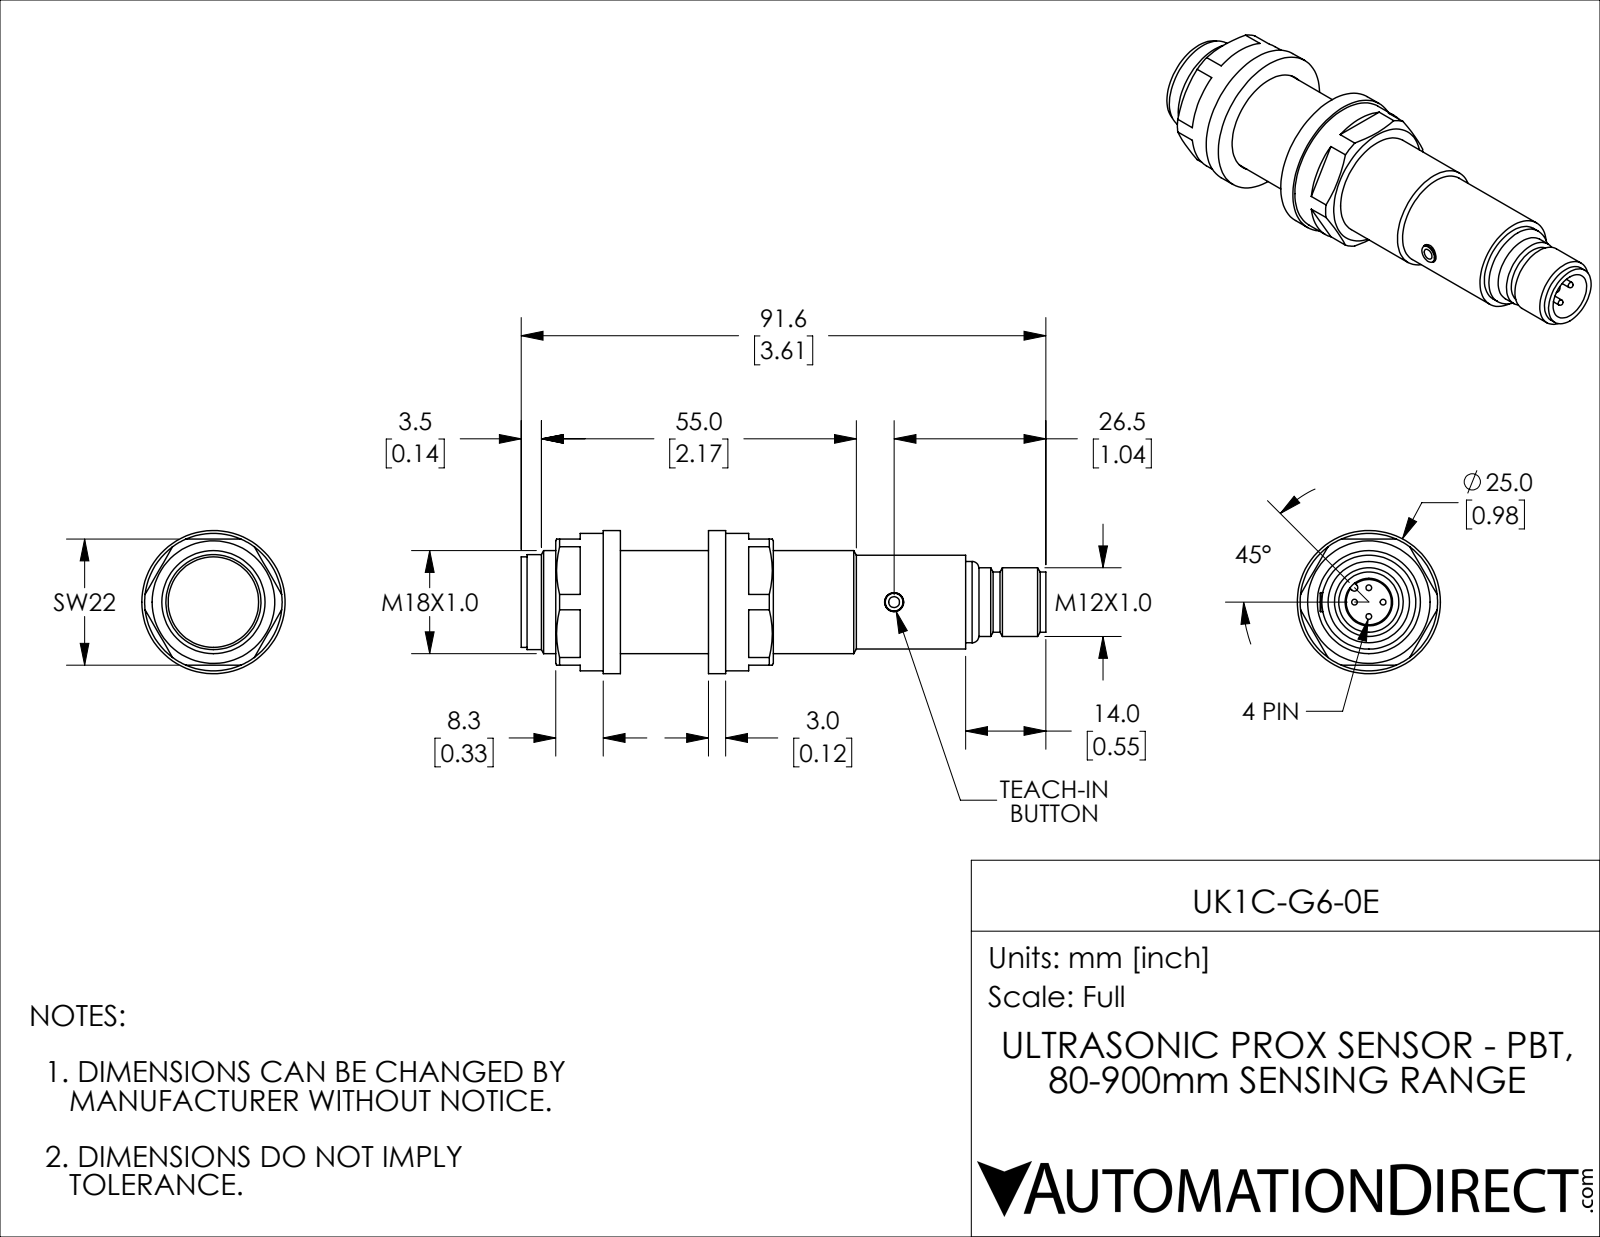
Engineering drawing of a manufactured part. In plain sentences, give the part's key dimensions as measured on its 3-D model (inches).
The part is named "UK1C-G6-0E". Its 3-D file was written by "SolidWorks 2018 (AUTOMOTIVE_DESIGN)". It is 6 solids with 123 faces: 43 planar, 49 cylindrical and 31 other. Overall it measures 3.606 by 0.984 by 0.984 inches. Its volume is 1.477 cubic inches and its surface area 16.01 square inches. Round holes: 1 of diameter 0.13, 1 of diameter 0.327, 1 of diameter 0.709, 1 of diameter 0.717. Round bosses or shafts: 4 of diameter 0.039, 1 of diameter 0.984, 1 of diameter 0.945, 1 of diameter 0.654, 1 of diameter 0.646, 1 of diameter 0.622, 1 of diameter 0.559, 1 of diameter 0.472. Partial cylindrical surfaces (rounded edges, fillets, slot ends): 1 of radius 0.024. The main face-to-face distances are 0.118, 0.724, 0.843, 0.606, 0.866, 0.327, 0.445, 1.051, 1.169, 0.563.
